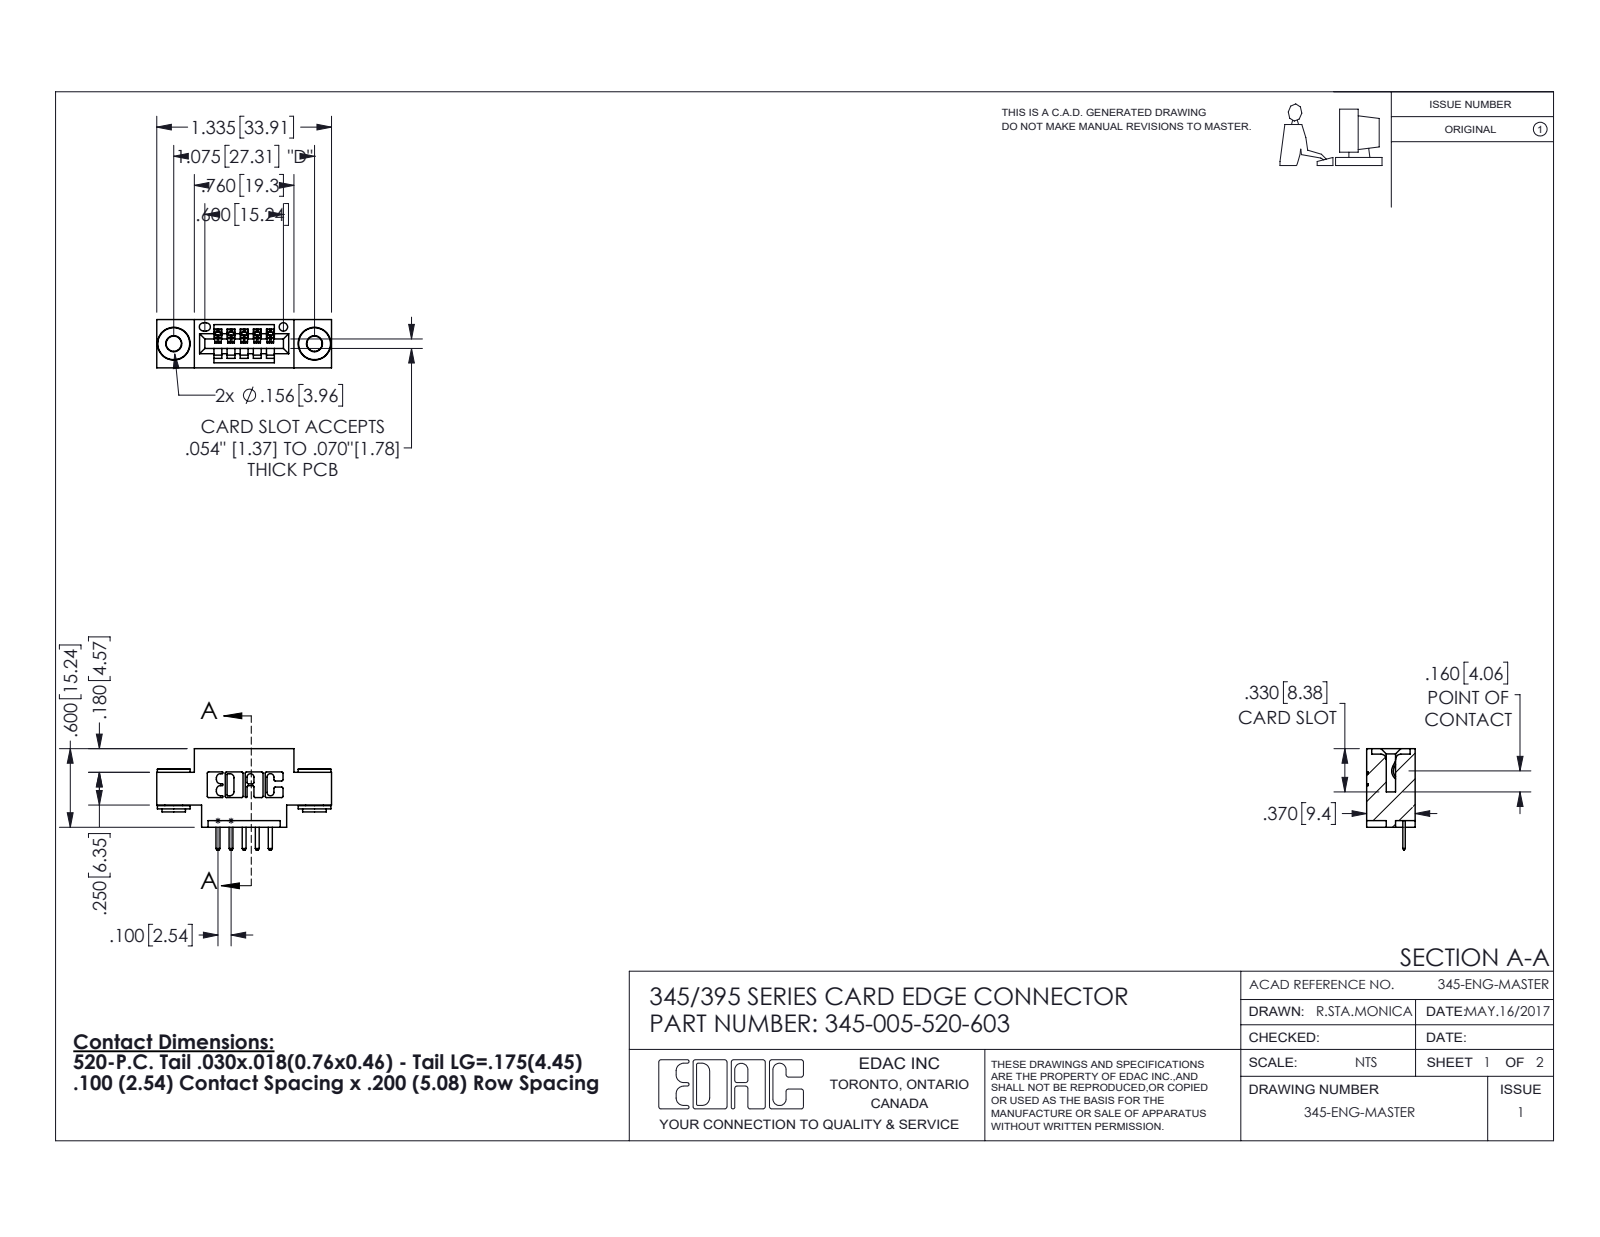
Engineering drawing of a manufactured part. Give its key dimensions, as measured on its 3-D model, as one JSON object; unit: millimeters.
{"part_name": "345-005-520-603; 345-250-002_345-250-002-102; 345 Part_0.170 Offset - 0.156 Dia-TH; 345-292-001_345-293-120", "step_written_by": "SolidWorks 2016 (CONFIG_CONTROL_DESIGN)", "units": "millimeters", "bodies": {"solids": 8, "faces": 478, "planar": 304, "cylindrical": 166, "other": 8}, "overall_size": [33.9, 19.7, 9.4], "volume_mm3": 2800, "surface_area_mm2": 3525, "round_holes": [[2.9, 2], [4, 2], [1.6, 1]], "round_bosses_or_shafts": [[6.4, 2], [4.6, 2], [3.5, 2]], "partial_cylinders_radius": [[0.3, 22], [0.3, 12], [0.2, 10], [0.2, 6], [0.8, 6], [0.7, 3], [0.8, 2], [1, 2]], "face_to_face_distances": [9.4, 5.1, 2.5, 1.8, 7.6, 6.4, 0.6, 1.5, 6.5, 14], "hole_center_spacings": [6.9, 21.5, 27.3]}
